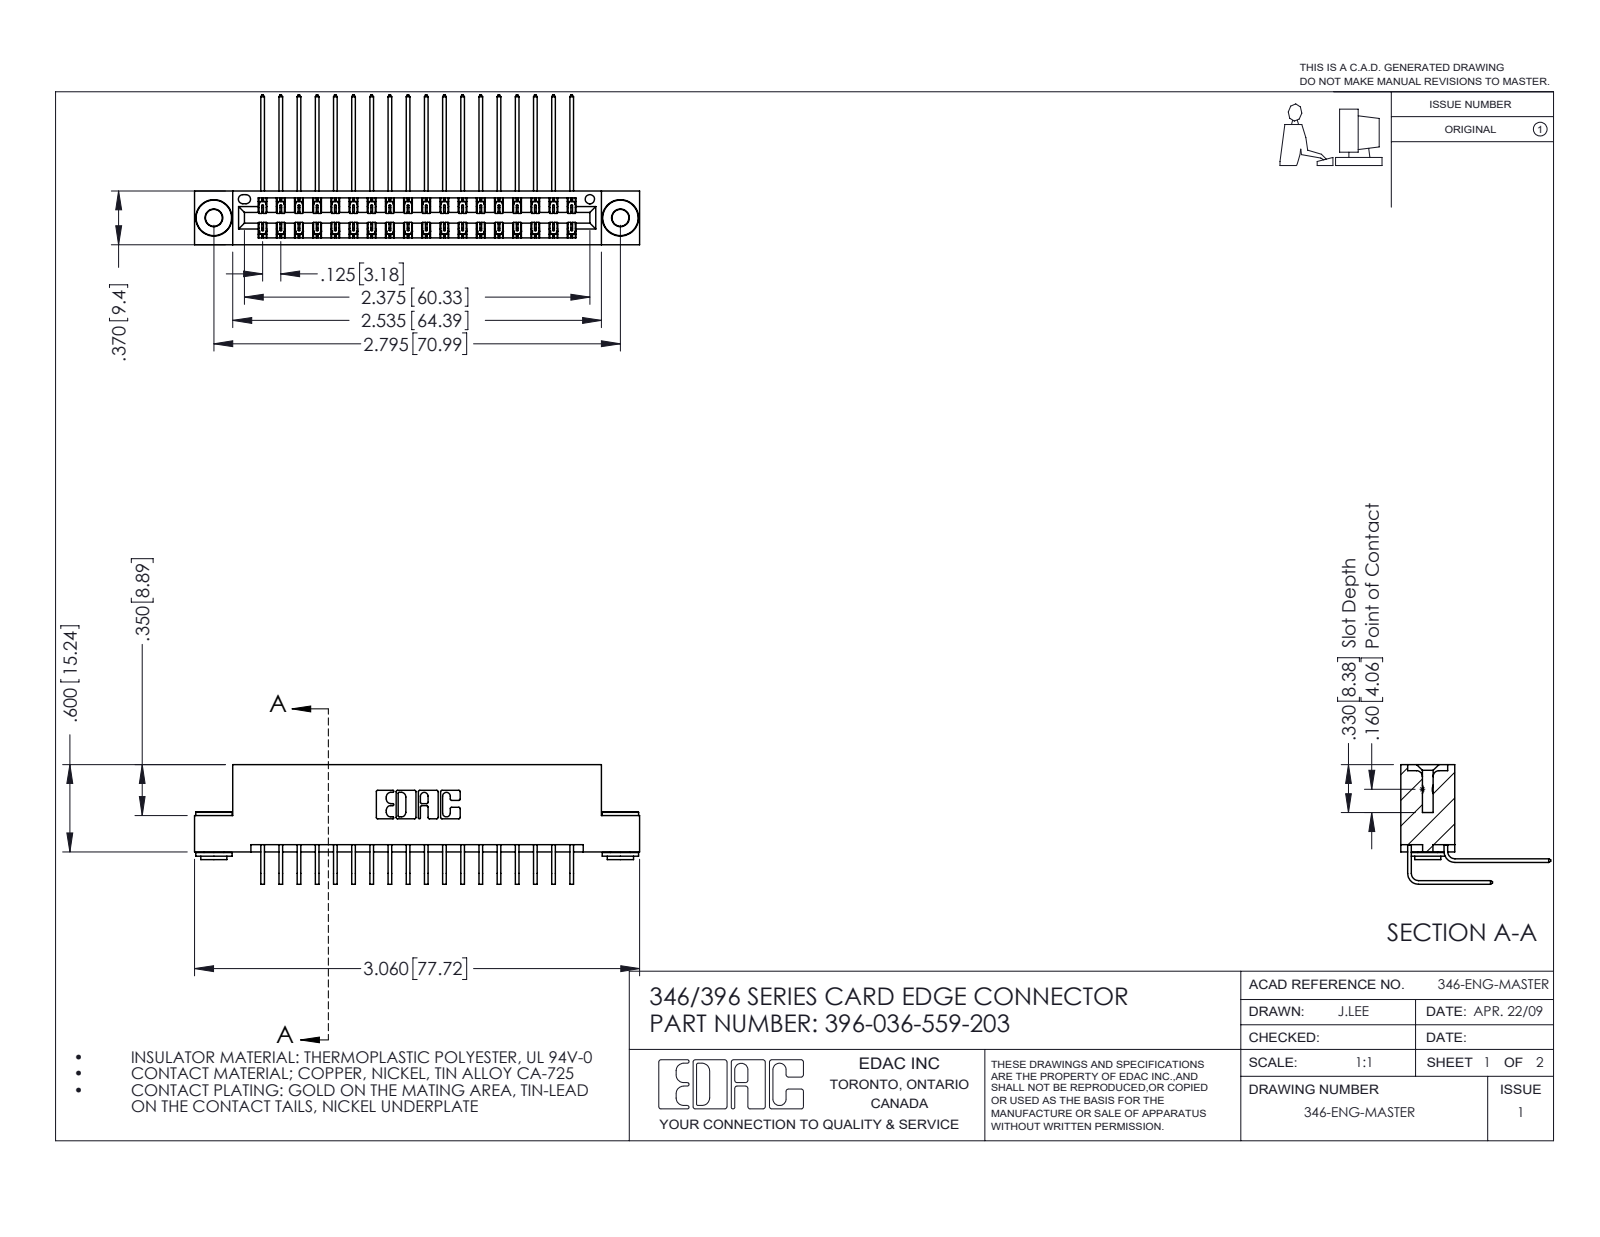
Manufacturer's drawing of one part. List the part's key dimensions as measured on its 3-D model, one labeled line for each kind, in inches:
Part name (STEP PRODUCT): 396-036-559-203; 345-292-001_559 Tail - 2; 345-292-001_558 559 Tail - 1; 346 Part_Flush Mounting Lugs - 0.156 Dia-TH (+1 more)
STEP written by: SolidWorks 2016 (CONFIG_CONTROL_DESIGN)
Units: inches
Bodies: 39 solids, 2104 faces (1418 planar, 678 cylindrical, 8 other)
Overall size (bounding box): 3.06 × 1.03 × 0.823
Volume: 0.465 in³ · Surface area: 17.53 in²
Round holes (diameter × count): ⌀0.116 ×2, ⌀0.156 ×2, ⌀0.064 ×1
Round bosses / shafts (diameter × count): ⌀0.25 ×2, ⌀0.18 ×2, ⌀0.136 ×2
Partial cylindrical surfaces — rounded edges, fillets, slot ends (radius × count): R0.006 ×54, R0.01 ×22, R0.007 ×6, R0.031 ×6, R0.026 ×3, R0.014 ×2, R0.022 ×2, R0.024 ×2
Main face-to-face distances: 0.048, 0.322, 0.25, 0.025, 0.37, 0.072, 0.298, 0.275, 0.148, 0.222
Hole centre spacings: 0.246, 2.588, 2.795
